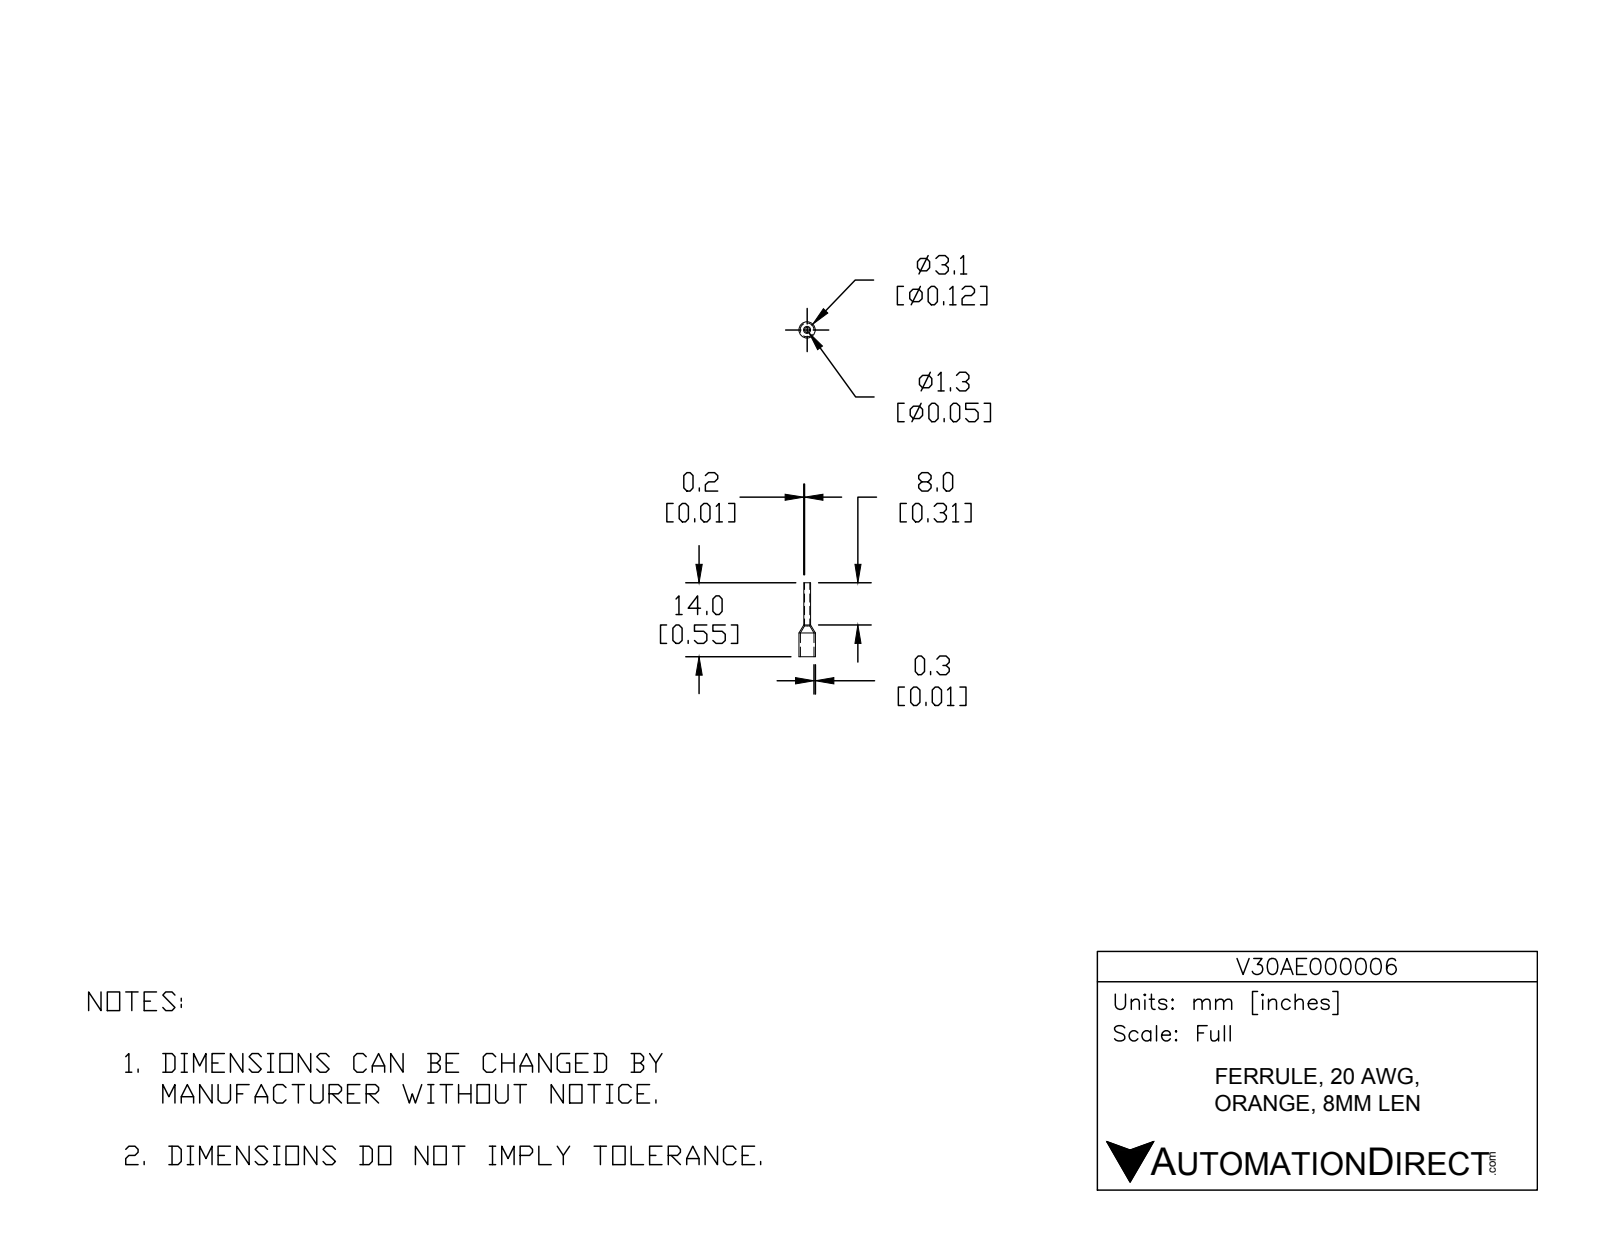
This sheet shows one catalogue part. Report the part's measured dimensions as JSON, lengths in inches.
{"part_name": "V30AE000006", "step_written_by": "SolidWorks 2017 (AUTOMOTIVE_DESIGN)", "units": "inches", "bodies": {"solids": 1, "faces": 14, "planar": 2, "cylindrical": 8, "other": 4}, "overall_size": [0.551, 0.122, 0.122], "volume_in3": 0.001, "surface_area_in2": 0.253, "round_holes": [[0.039, 1], [0.102, 1]], "round_bosses_or_shafts": [[0.122, 1], [0.051, 1]], "face_to_face_distances": [0.551]}
